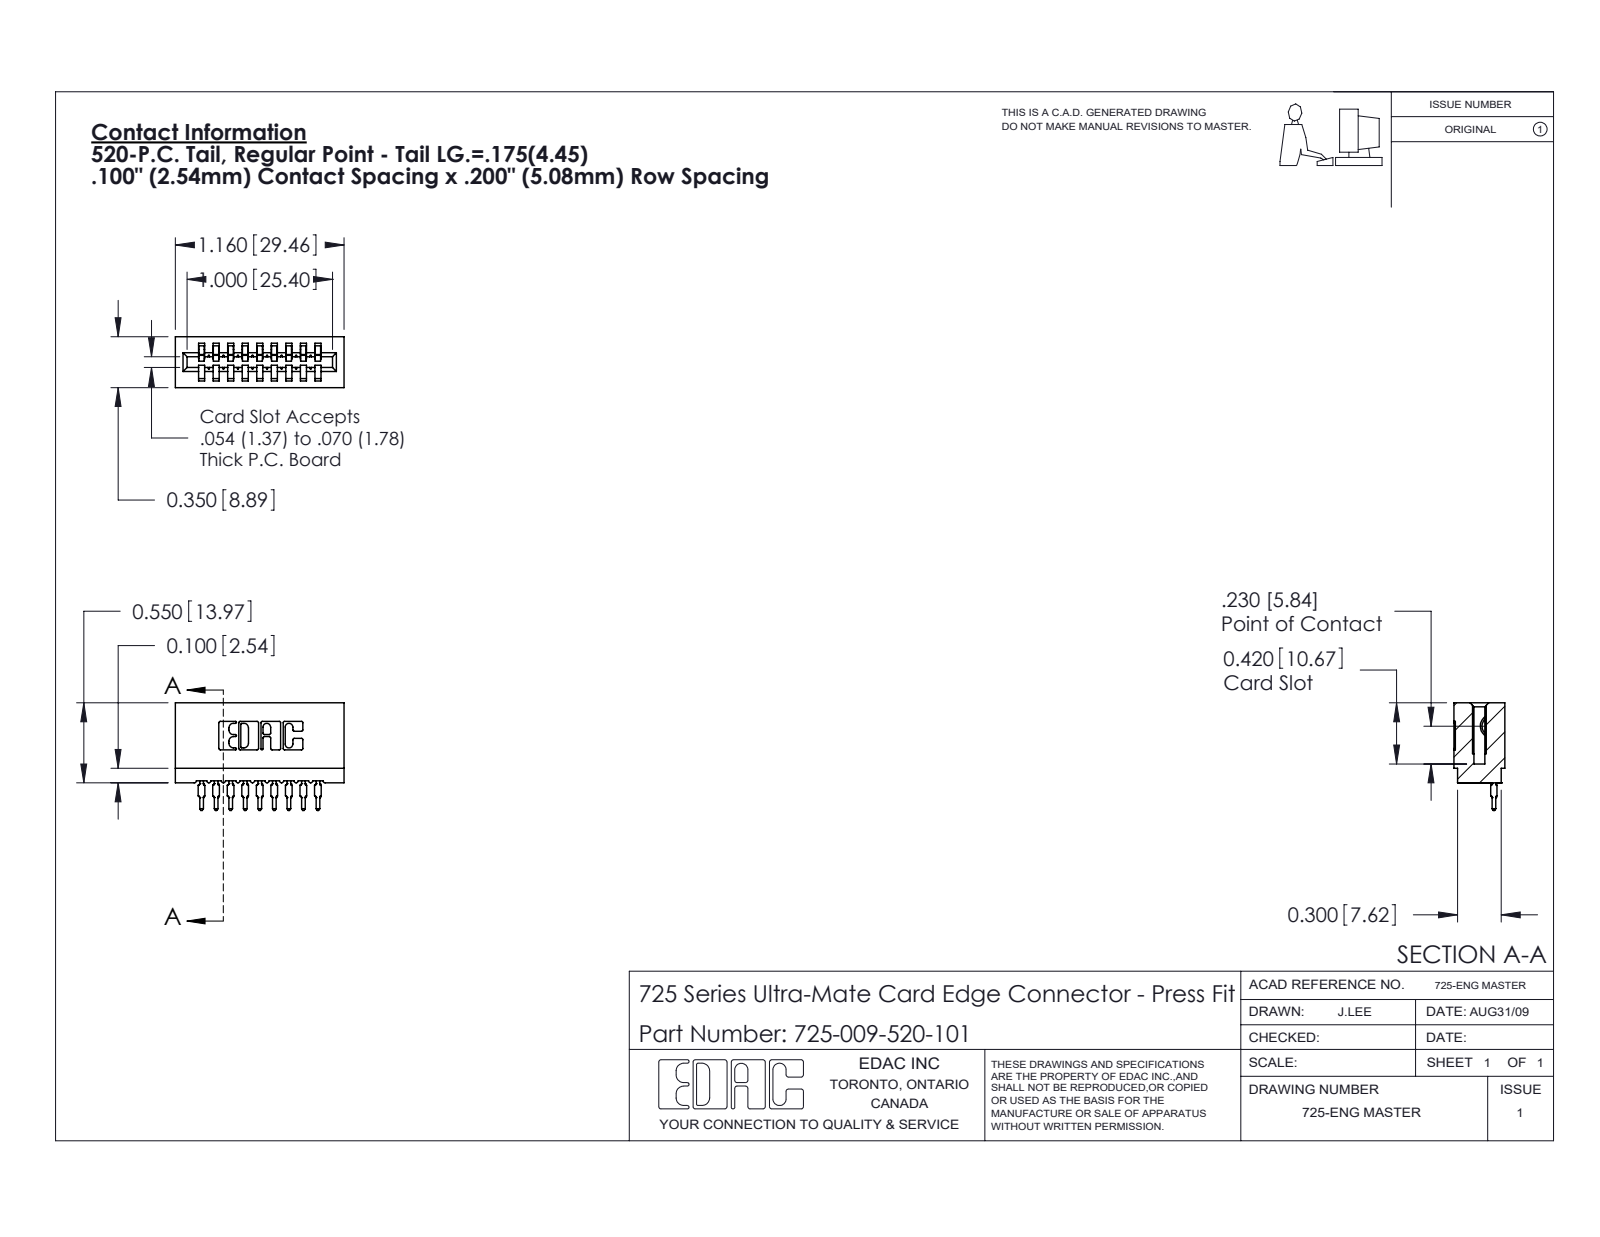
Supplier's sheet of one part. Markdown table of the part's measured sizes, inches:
| quantity | value |
| --- | --- |
| part name | 725 Part_Insulator Option - 01; 745-292-001_520; 725-009-520-101 |
| STEP written by | SolidWorks 2020 (CONFIG_CONTROL_DESIGN) |
| units | inches |
| bodies | 10 solids, 1103 faces (658 planar, 211 cylindrical, 234 other) |
| overall size | 1.16 × 0.741 × 0.35 |
| volume | 0.147 in³ |
| surface area | 6.176 in² |
| partial cylindrical surfaces (radius × count) | 0.01 × 22, 0.015 × 18, 0.021 × 18, 0.007 × 6, 0.031 × 6, 0.005 × 4, 0.011 × 4, 0.026 × 3 |
| main face-to-face distances | 0.1, 0.2, 0.3, 0.4, 0.042, 0.5, 0.142, 0.058, 0.242, 0.158 |
